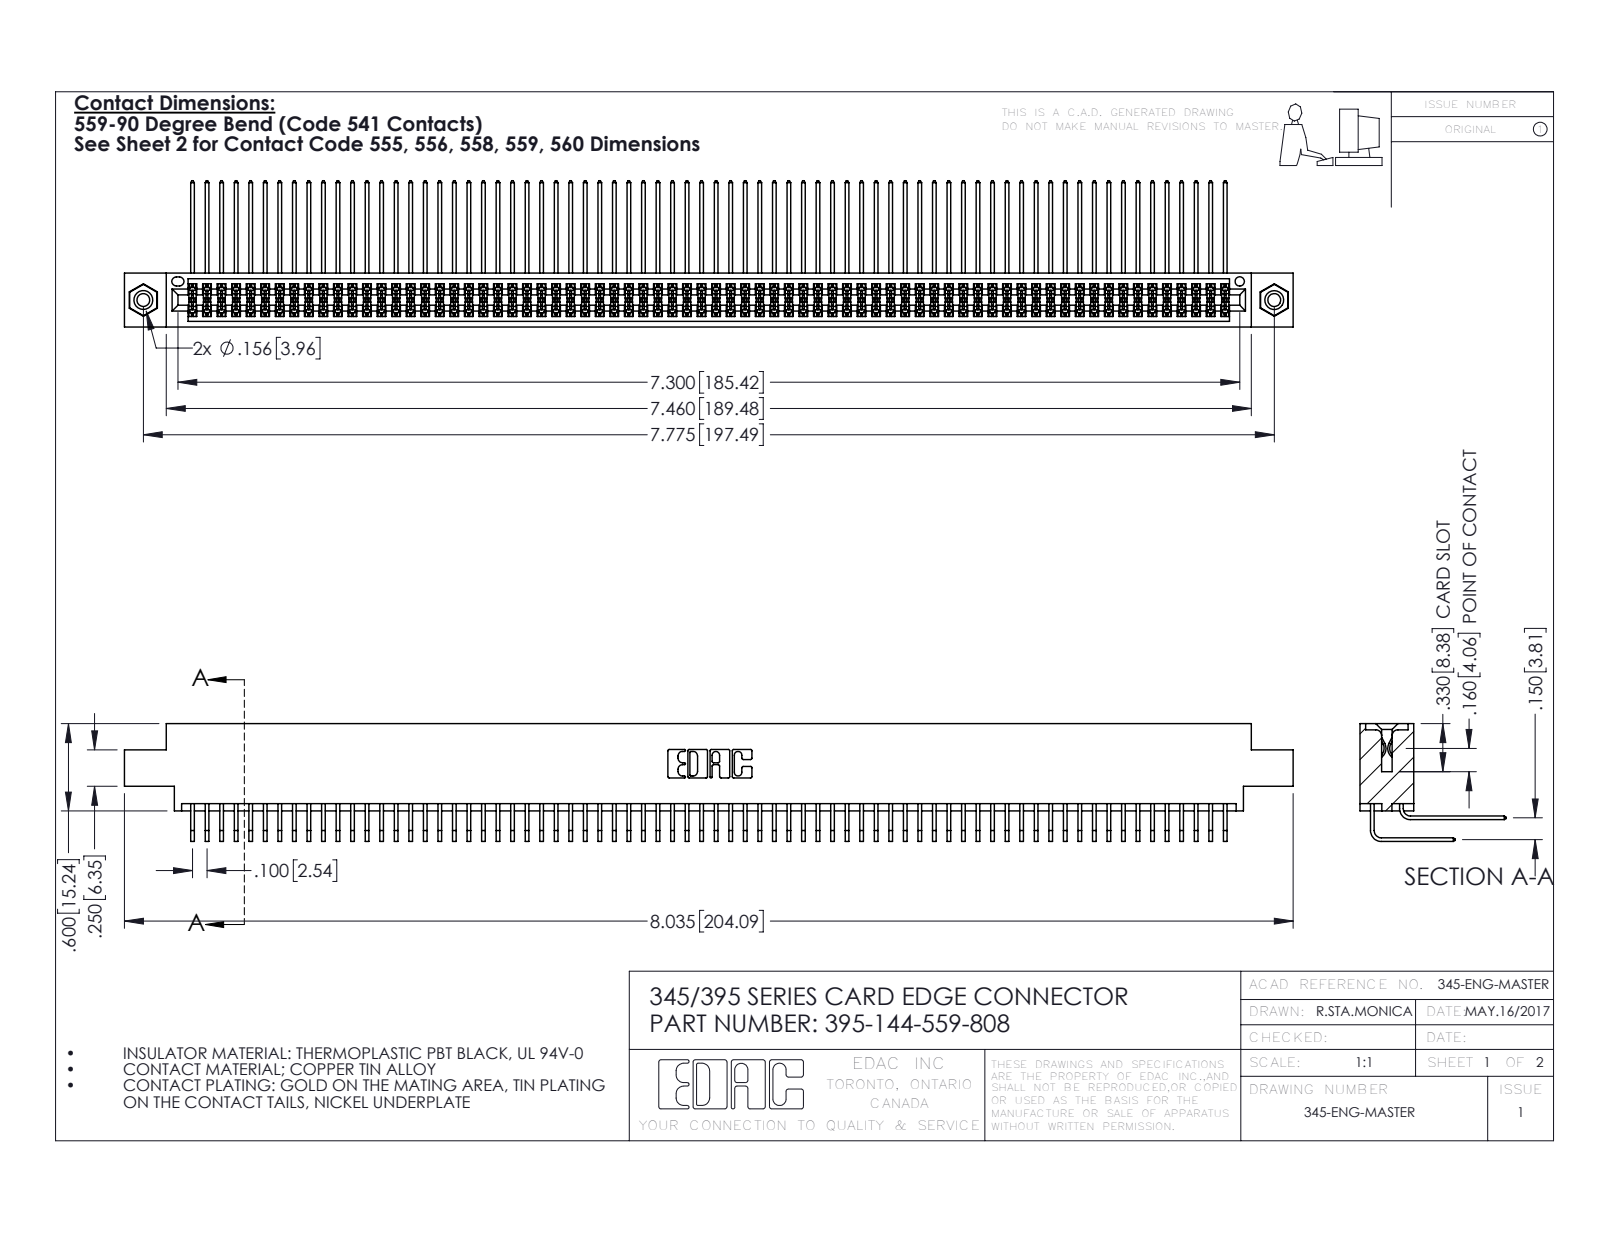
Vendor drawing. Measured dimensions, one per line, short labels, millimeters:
name: 345-250-001_345-250-003-102; 345 Part_0.170 Offset - 0.156 Dia-TI; 395-144-559-808; 345-292-001_559 Tail - 2 (+1 more)
written by: SolidWorks 2016 (CONFIG_CONTROL_DESIGN)
unit: mm
bodies: 147 solids, 7678 faces (5156 planar, 2506 cylindrical, 16 other)
size: 204.1 × 25.5 × 20.5
volume: 20 810 mm³; area: 35 410 mm²
holes: 2× ⌀2.3, 2× ⌀3.2, 2× ⌀4, 1× ⌀1.6
bosses: 2× ⌀3.9
rounds: 217× R0.2, 22× R0.3, 6× R0.2, 6× R0.8, 3× R0.7, 2× R0.4, 2× R0.5, 2× R0.6
face distances: 1.8, 7.6, 5.1, 9.4, 2.5, 6.9, 0.6, 5.7, 4.4, 3.8
hole spacings: 6.9, 191.5, 197.5
